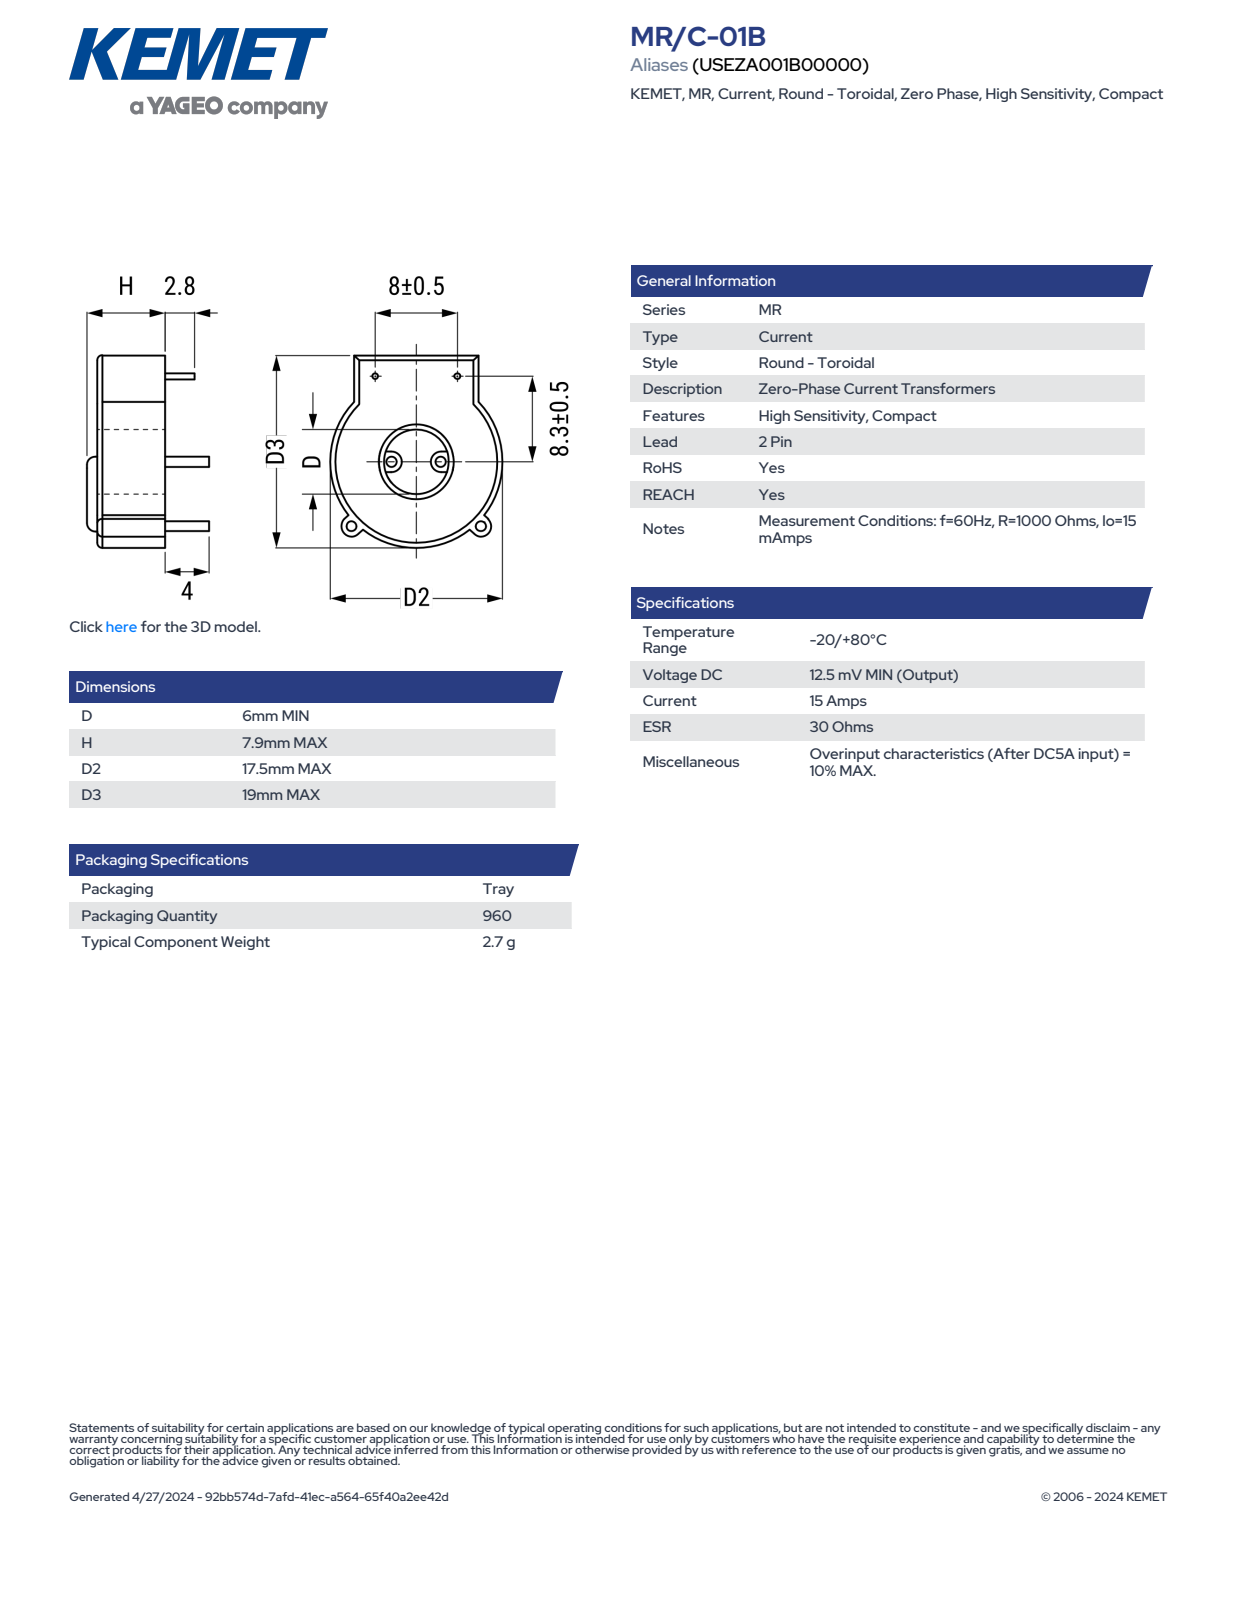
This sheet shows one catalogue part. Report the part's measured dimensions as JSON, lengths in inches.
{"part_name": "SC_MRC01_D6H6.7D217.5D319", "step_written_by": "SolidWorks 2014 (AUTOMOTIVE_DESIGN)", "units": "inches", "bodies": {"solids": 1, "faces": 151, "planar": 41, "cylindrical": 49, "other": 61}, "overall_size": [0.748, 0.689, 0.469], "volume_in3": 0.102, "surface_area_in2": 1.852, "round_bosses_or_shafts": [[0.039, 6], [0.026, 2]], "partial_cylinders_radius": [[0.012, 13], [0.035, 4], [0.118, 1], [0.344, 1], [0.344, 1]], "face_to_face_distances": [0.264, 0.417, 0.069, 0.369, 0.438, 0.157, 0.421, 0.047, 0.11, 0.374]}
